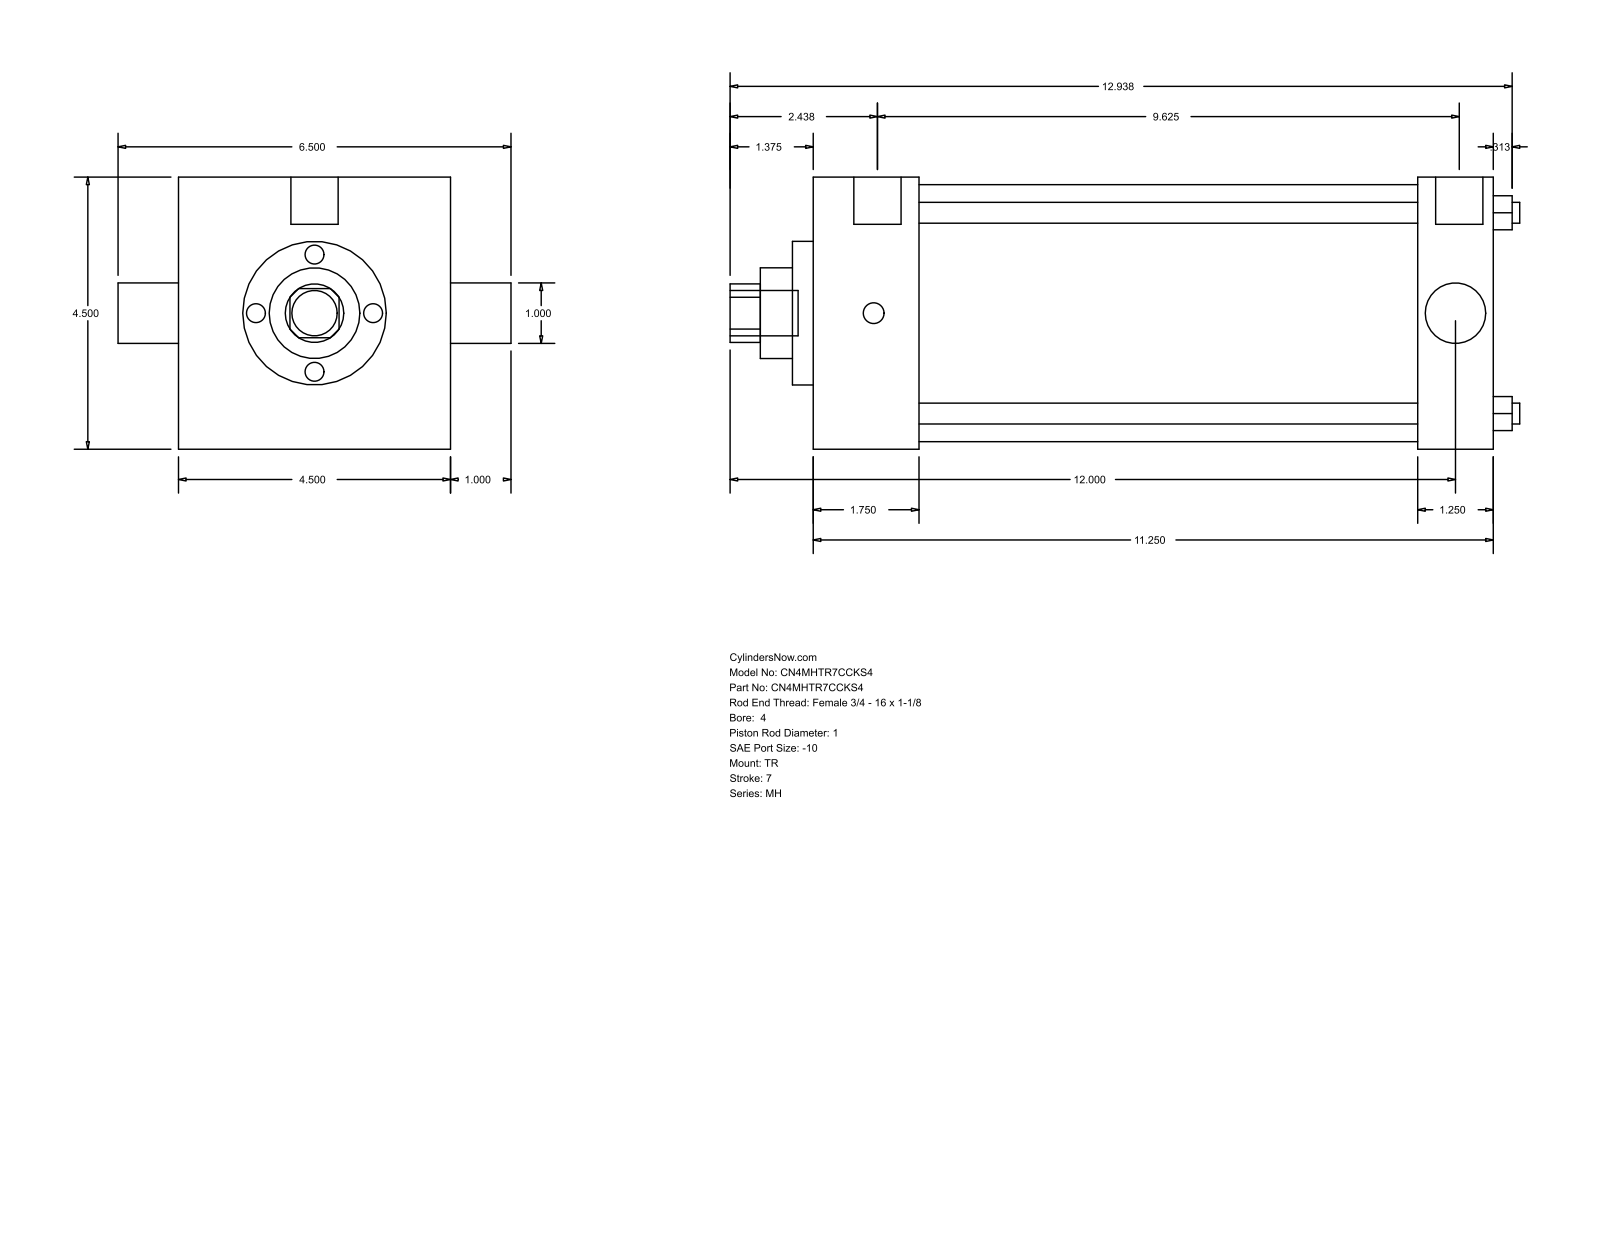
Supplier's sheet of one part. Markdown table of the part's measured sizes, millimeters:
| quantity | value |
| --- | --- |
| part name | MH_TR__0400_1 |
| STEP written by | GSSL Pune (CONFIG_CONTROL_DESIGN) |
| units | millimeters |
| bodies | 0 solids, 86 faces (61 planar, 25 cylindrical, 0 other) |
| overall size | 331.79 × 165.1 × 114.3 |
| round holes (diameter × count) | 8.76 × 4, 25.4 × 2, 38.1 × 1, 60.33 × 1, 107.95 × 1 |
| round bosses / shafts (diameter × count) | 8.73 × 3, 19.84 × 2, 19.05 × 1 |
| partial cylindrical surfaces (radius × count) | 12.29 × 1 |
| main face-to-face distances | 114.3, 285.76, 44.46, 241.3, 254.01, 209.55, 31.75, 8.73, 53.19, 262.74 |
| hole center spacings | 59.62, 84.32, 119.25 |
